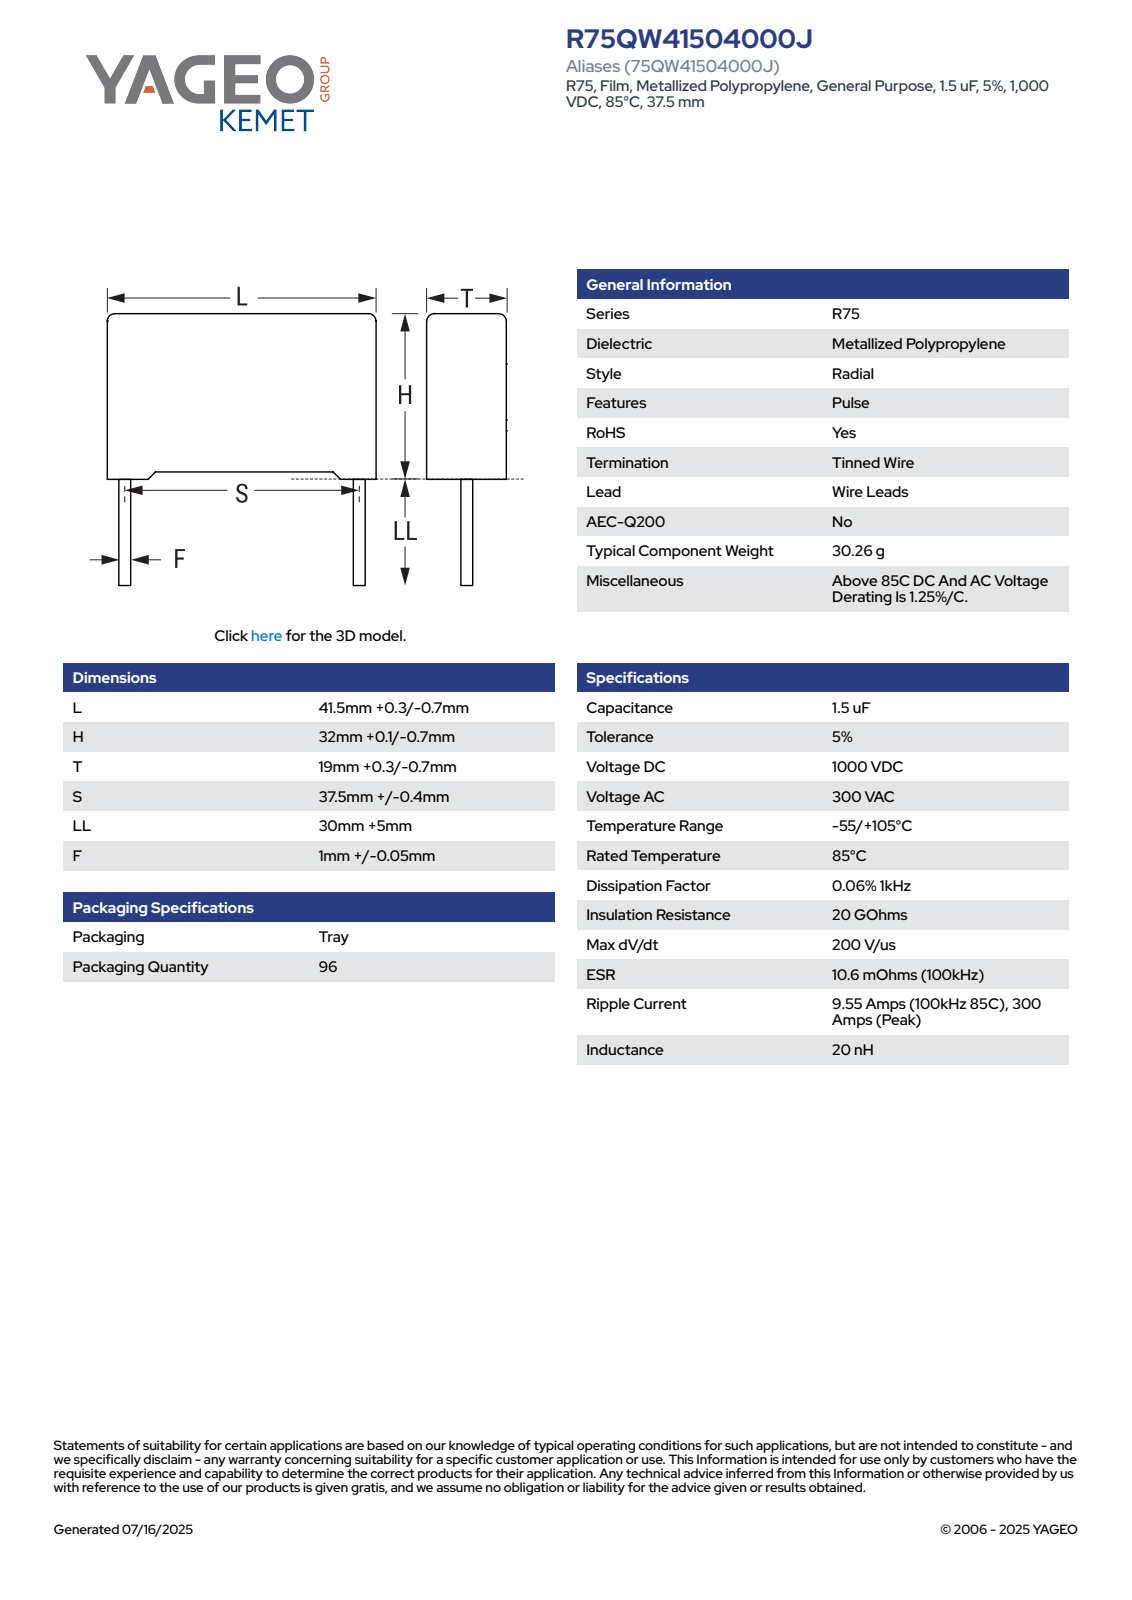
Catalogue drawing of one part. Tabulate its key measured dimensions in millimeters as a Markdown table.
| quantity | value |
| --- | --- |
| part name | CFR_RB2_41.5X32X19_L41.8H32.1T19.3S37.5LL35F1.05 |
| STEP written by | SolidWorks 2021 (AUTOMOTIVE_DESIGN) |
| units | millimeters |
| bodies | 4 solids, 85 faces (77 planar, 8 cylindrical, 0 other) |
| overall size | 67.1 × 41.8 × 19.3 |
| volume | 25 174 mm³ |
| surface area | 5 842 mm² |
| round bosses / shafts (diameter × count) | 1.05 × 2 |
| partial cylindrical surfaces (radius × count) | 0.5 × 4 |
| main face-to-face distances | 19.3, 30.99, 41.8, 0.36, 31.35, 0.75, 1.11, 32.1, 1.39, 19.31 |
